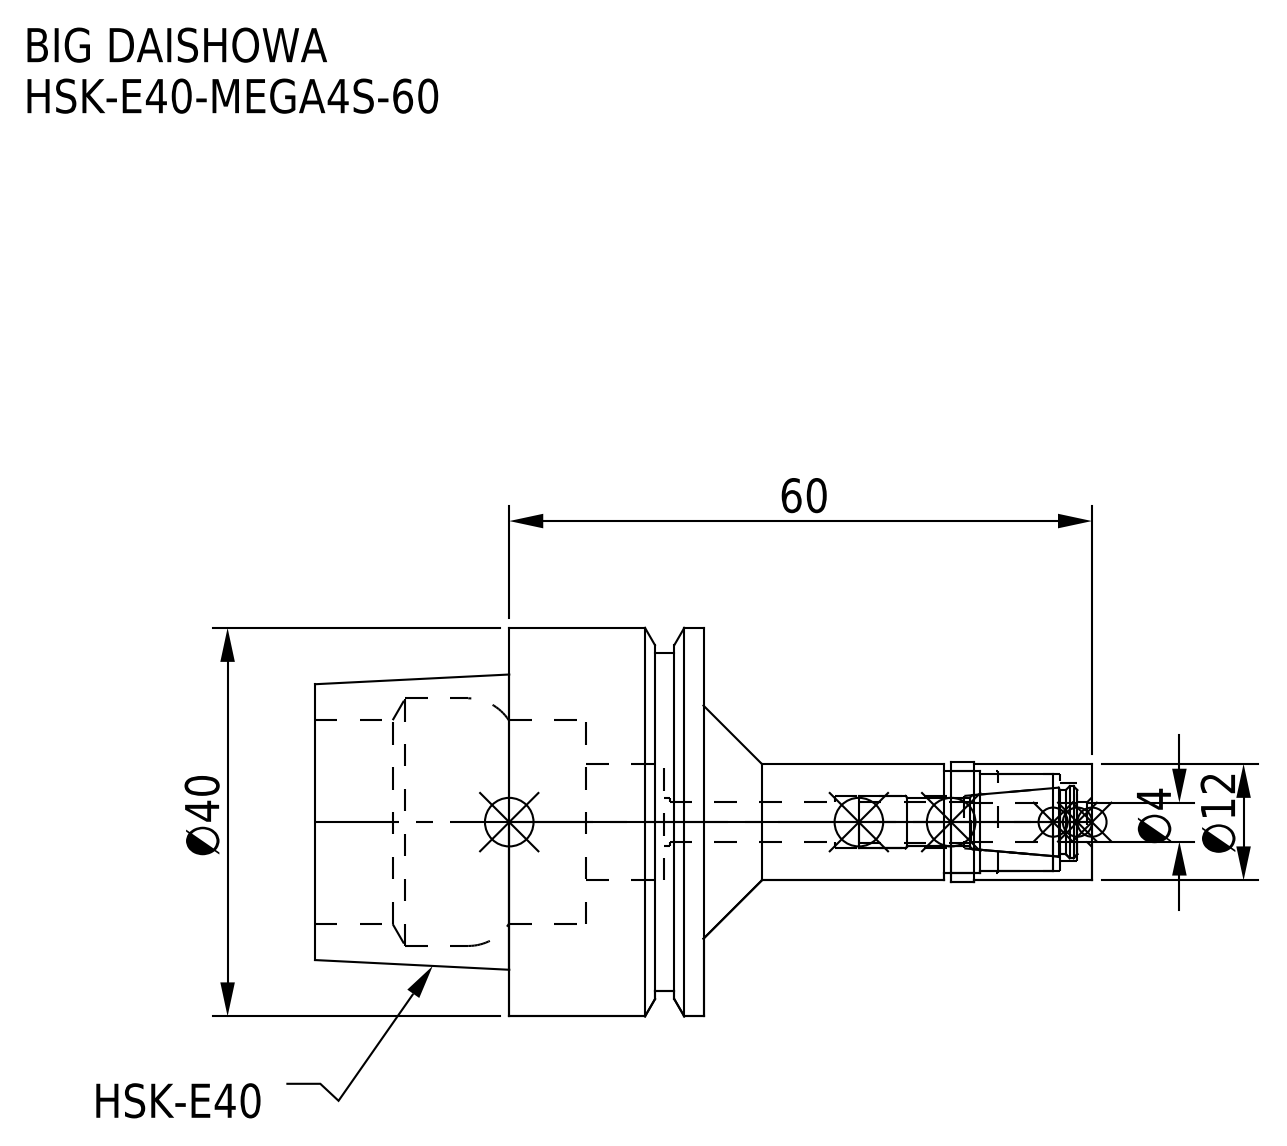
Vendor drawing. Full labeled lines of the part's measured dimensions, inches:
Part name (STEP PRODUCT): MGN4S_1.stp; HSK-E40-MEGA4S-60-040-FreeParts; HE40MS04060-040_ASM.stp; HSK-E40-MEGA4S-60-040.stp (+3 more)
STEP written by: SolidWorks 2019 (CONFIG_CONTROL_DESIGN)
Units: inches
Bodies: 2 solids, 74 faces (18 planar, 40 cylindrical, 16 other)
Overall size (bounding box): 3.15 × 1.575 × 1.575
Volume: 1.836 in³ · Surface area: 19.51 in²
Round holes (diameter × count): ⌀0.161 ×1, ⌀0.197 ×1, ⌀0.213 ×1, ⌀0.315 ×1, ⌀0.394 ×1, ⌀0.413 ×1, ⌀0.827 ×1, ⌀1.004 ×1
Round bosses / shafts (diameter × count): ⌀1.575 ×1, ⌀1.37 ×1, ⌀0.484 ×1, ⌀0.472 ×1
Main face-to-face distances: 0.787, 1.575, 0.474, 0.313, 1.1, 0.118, 0.591, 0.669, 0.159, 0.315
